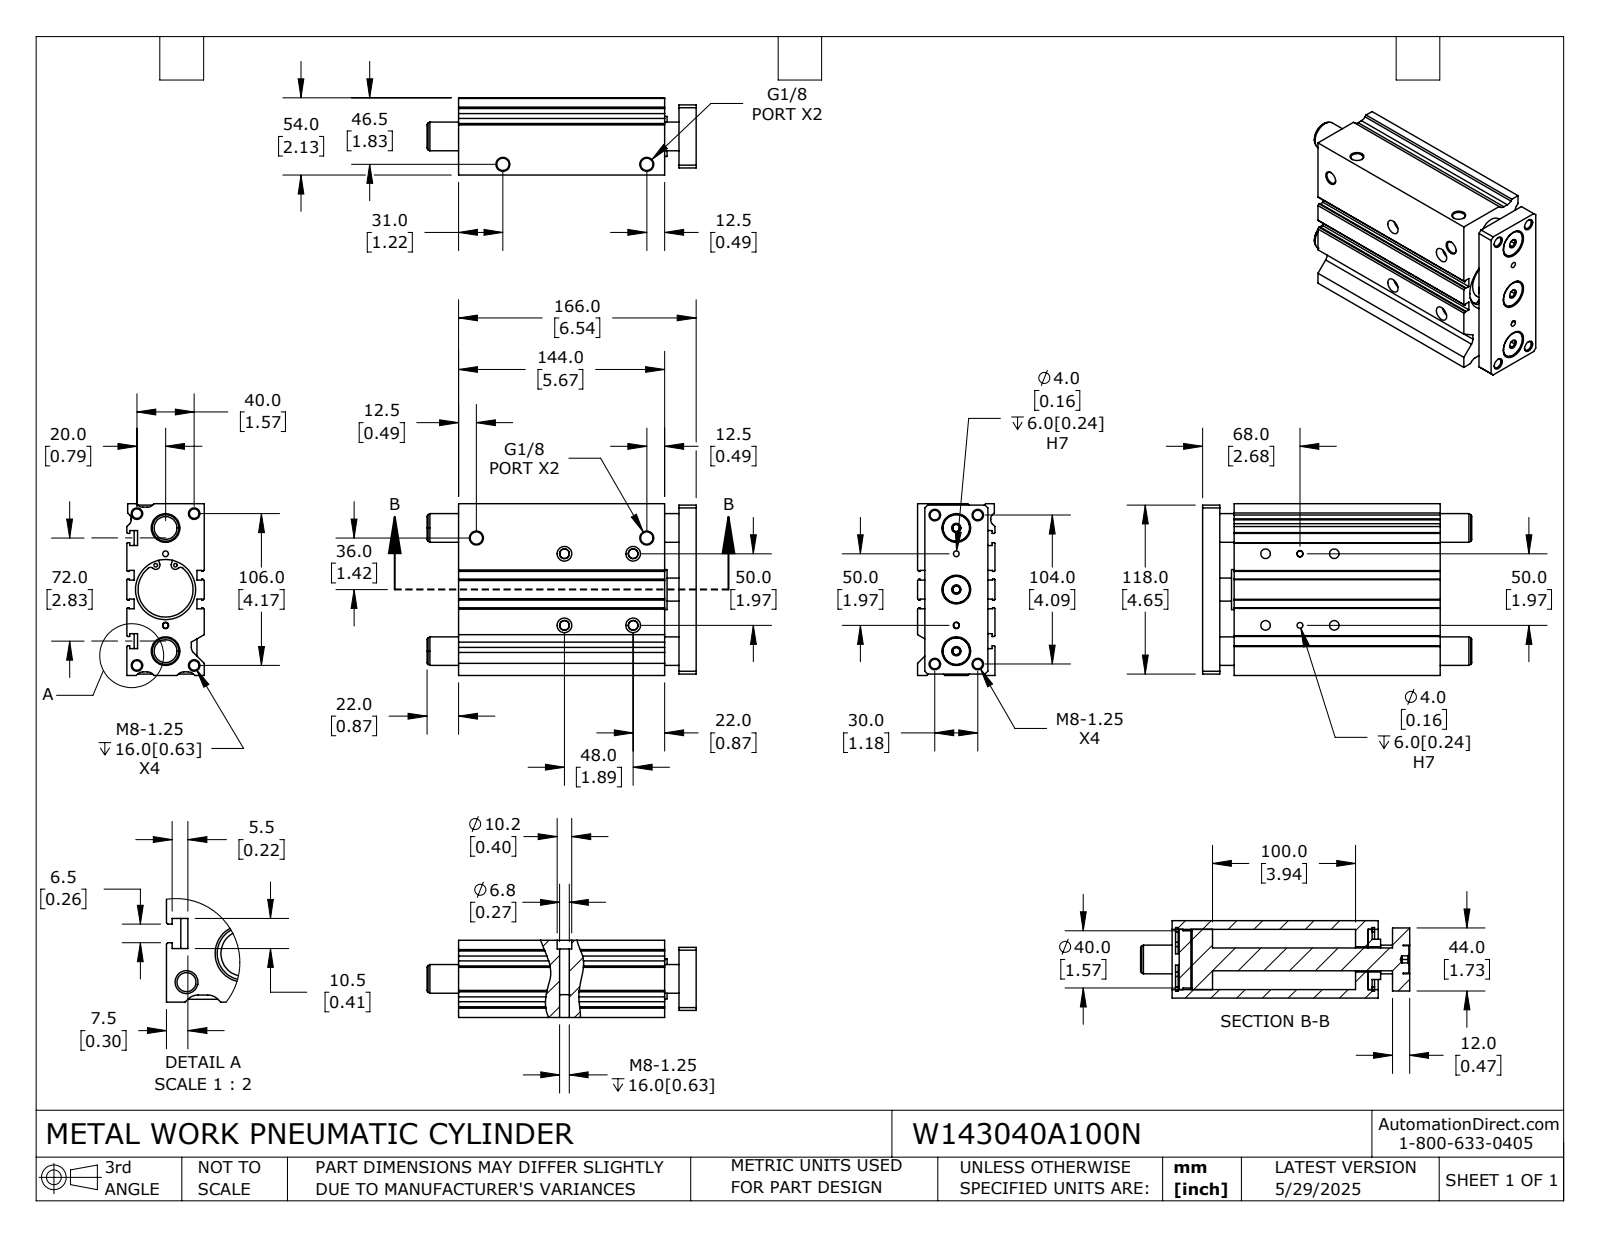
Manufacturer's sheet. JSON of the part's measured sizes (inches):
{"part_name": "W143040A100N_BODY; W143040A100N; W143040A100N_ROD", "step_written_by": "SolidWorks 2024 (CONFIG_CONTROL_DESIGN)", "units": "inches", "bodies": {"solids": 6, "faces": 393, "planar": 192, "cylindrical": 151, "other": 50}, "overall_size": [7.402, 4.724, 2.126], "volume_in3": 49.1, "surface_area_in2": 277.4, "round_holes": [[0.262, 12], [0.098, 4], [0.157, 4], [0.268, 4], [0.337, 4], [0.402, 4], [0.197, 3], [0.787, 3], [0.697, 1], [1.51, 1]], "round_bosses_or_shafts": [[0.748, 3], [1.752, 2], [1.654, 1], [1.575, 1], [1.102, 1], [0.63, 1]], "partial_cylinders_radius": [[0.197, 7], [0.079, 4], [0.089, 4], [0.116, 4], [0.157, 2]], "face_to_face_distances": [2.126, 0.197, 1.929, 0.098, 0.866, 4.724, 6.535, 0.472, 0.394, 6.063], "hole_center_spacings": [0.201, 0.415, 0.689, 0.722, 0.88, 0.945, 1.059, 1.216]}
